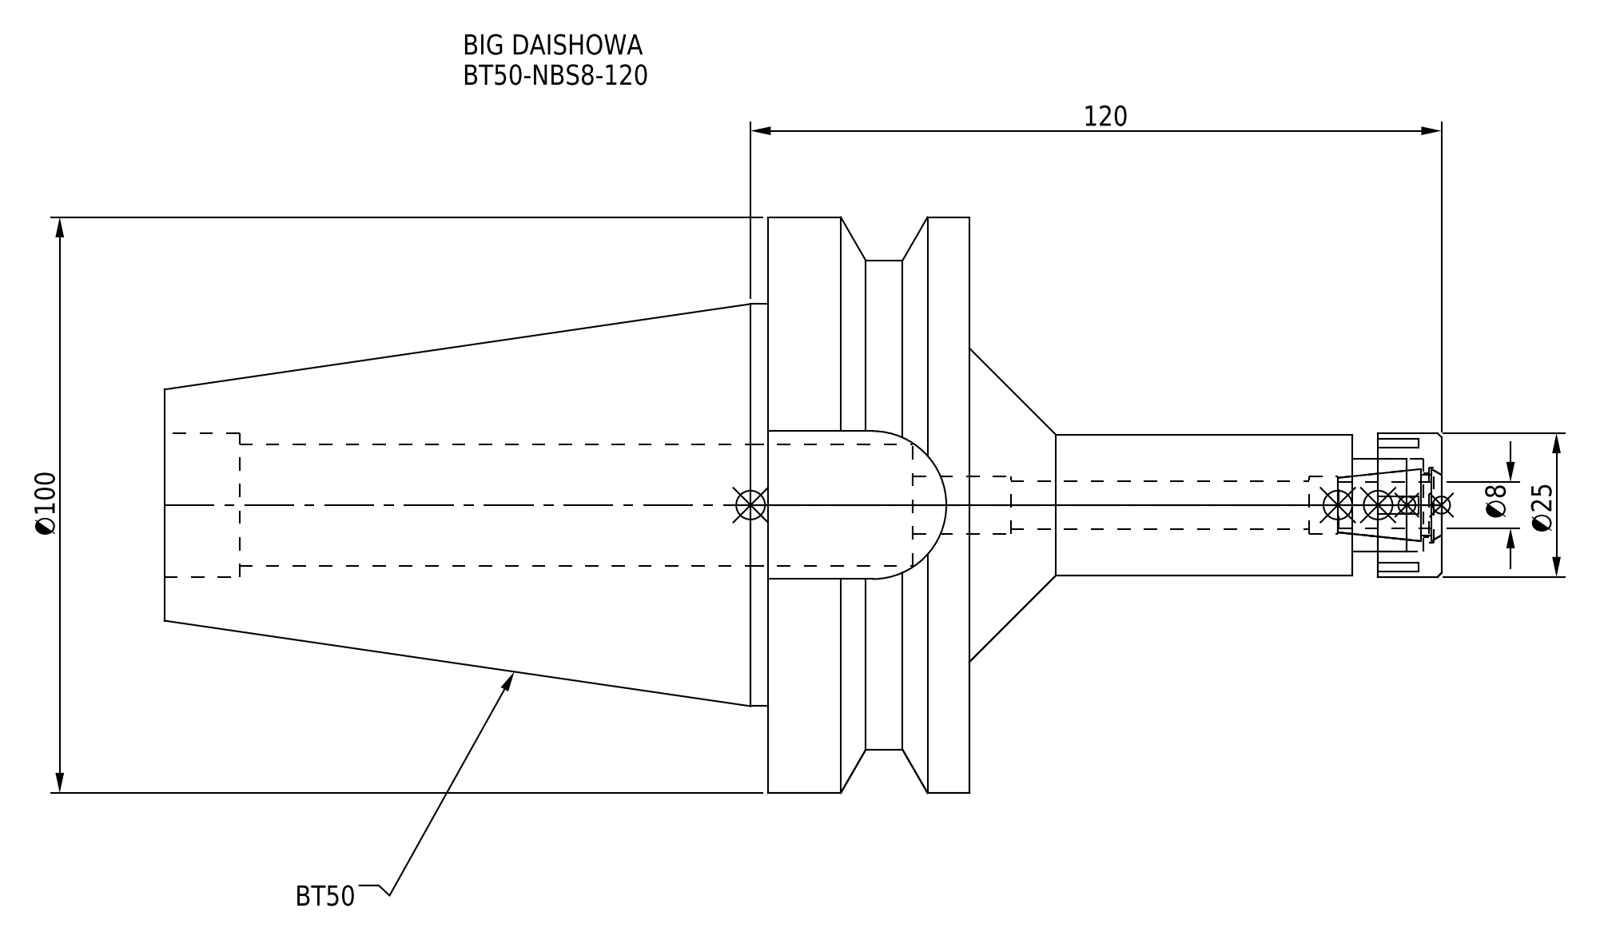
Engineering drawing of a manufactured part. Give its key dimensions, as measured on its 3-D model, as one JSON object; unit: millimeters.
{"part_name": "NBN8_1.stp; BT50-NBS8-120-FreeParts; DXF_TEMP_ASSY_ASM_4_ASM.stp; BT50-NBS8-120_1.stp (+3 more)", "step_written_by": "SolidWorks 2019 (CONFIG_CONTROL_DESIGN)", "units": "millimeters", "bodies": {"solids": 2, "faces": 93, "planar": 45, "cylindrical": 34, "other": 14}, "overall_size": [221.8, 100, 100], "volume_mm3": 489399, "surface_area_mm2": 63811, "round_holes": [[8.4, 1], [10, 1], [11, 1], [13, 1], [16, 1], [21.2, 1], [25, 1]], "round_bosses_or_shafts": [[100, 1], [85, 1], [69.85, 1], [24.5, 1]], "partial_cylinders_radius": [[12.85, 1]], "face_to_face_distances": [35, 139.8, 104.8, 70.8, 117, 25.7, 91.8, 82, 221.8, 9.8]}
